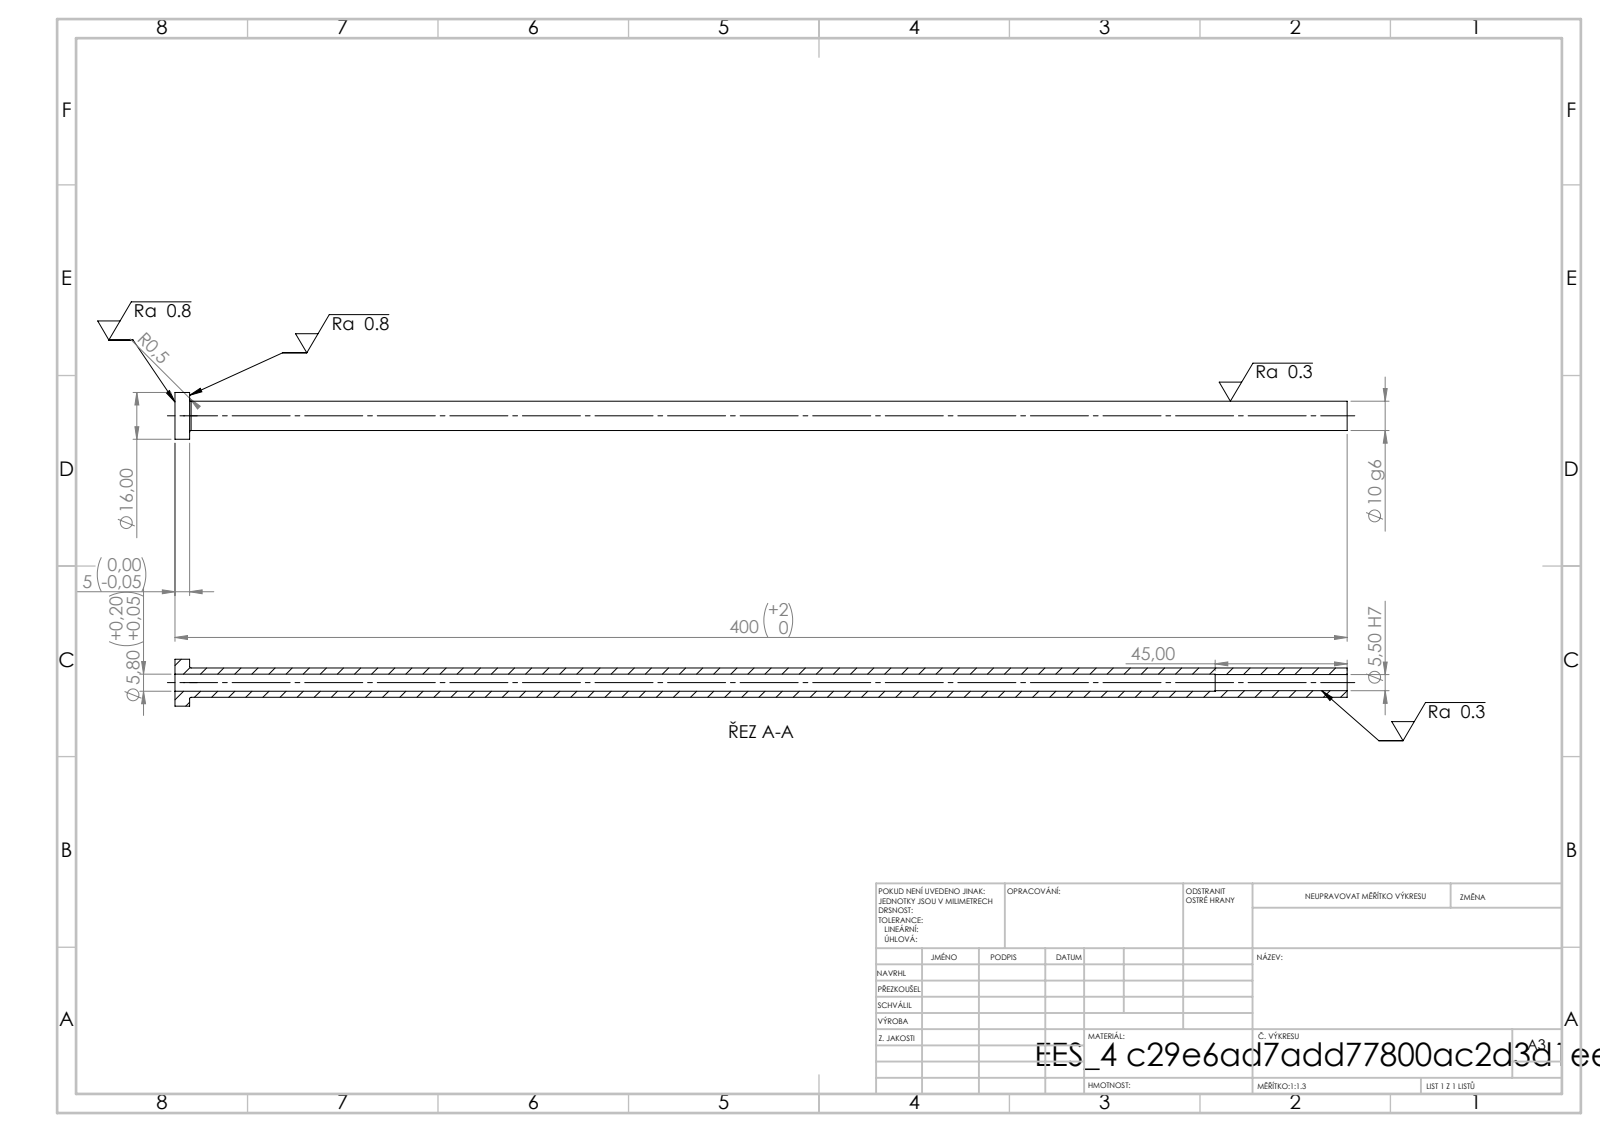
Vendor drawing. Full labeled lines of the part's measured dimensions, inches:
STEP written by: SolidWorks 2019 (CONFIG_CONTROL_DESIGN)
Units: inches
Bodies: 1 solid, 14 faces (4 planar, 8 cylindrical, 2 other)
Overall size (bounding box): 15.748 × 0.63 × 0.63
Volume: 1.317 in³ · Surface area: 31.4 in²
Round holes (diameter × count): ⌀0.217 ×1, ⌀0.228 ×1
Round bosses / shafts (diameter × count): ⌀0.63 ×1, ⌀0.394 ×1
Main face-to-face distances: 0.197, 15.748, 15.551, 13.976, 13.78, 1.772
